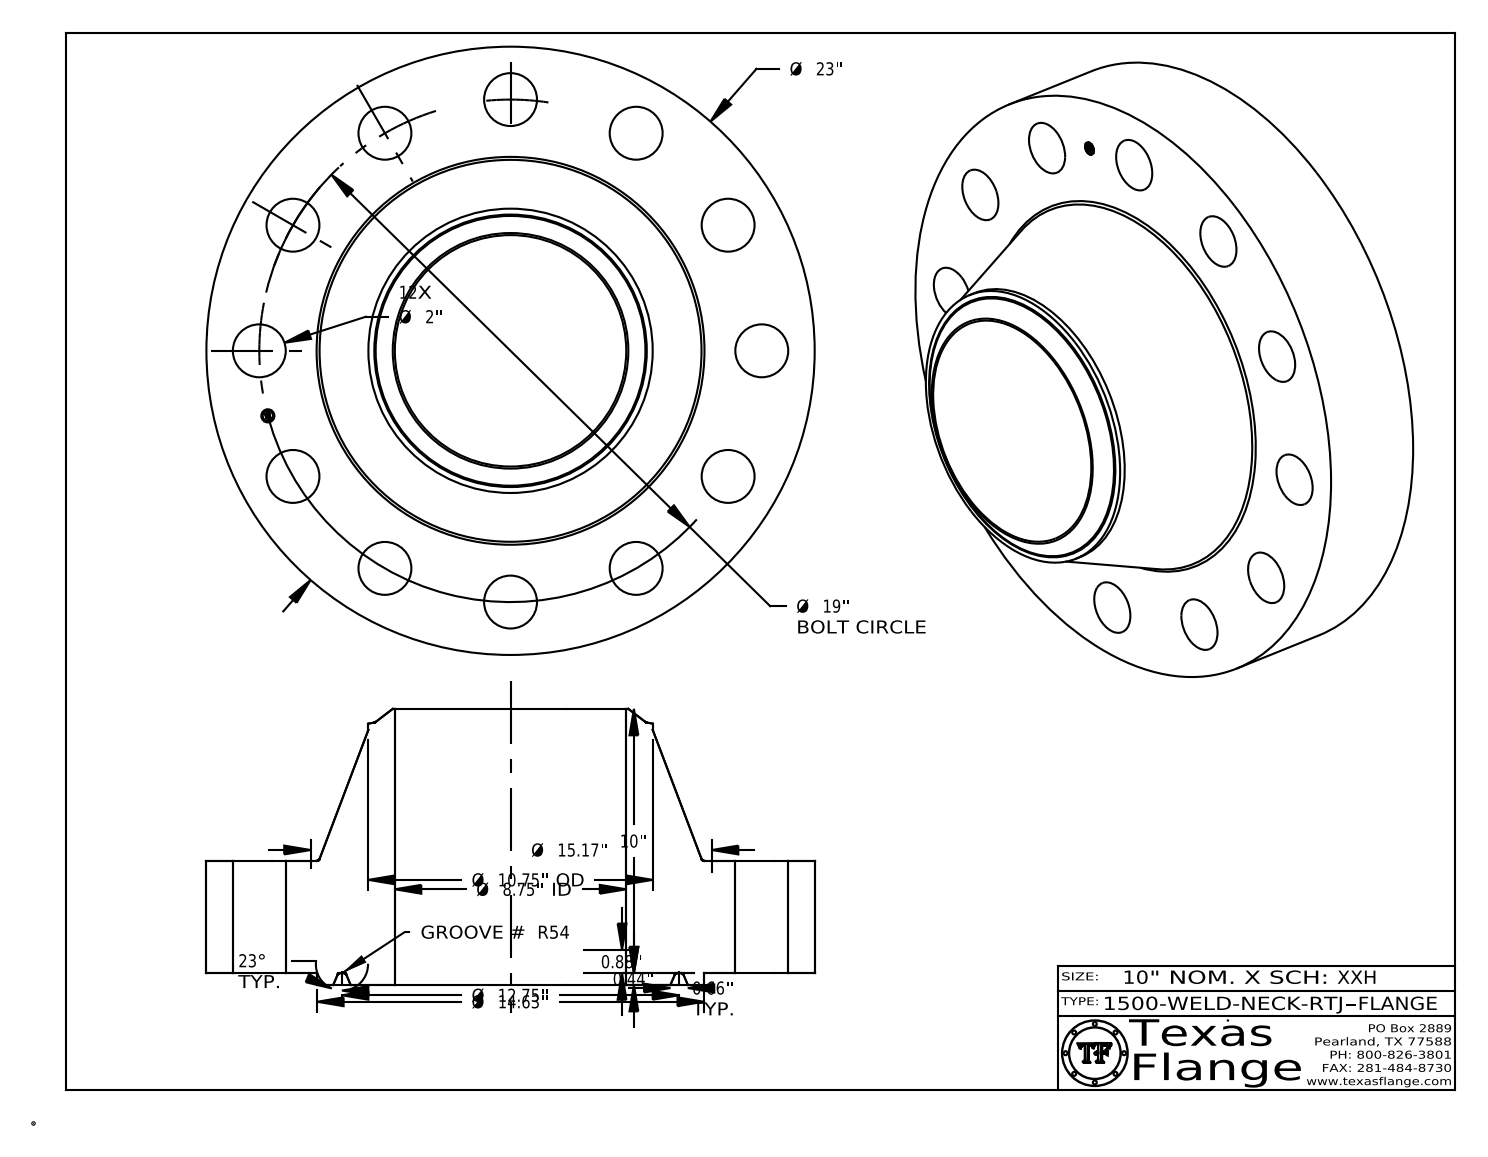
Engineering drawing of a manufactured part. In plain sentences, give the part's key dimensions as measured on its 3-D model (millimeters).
The part is named "1500-WELD-NECK-RTJ". Its 3-D file was written by "CATIA V5 STEP AP214 (AUTOMOTIVE_DESIGN)". It is 1 solid with 441 faces: 371 planar, 52 cylindrical and 18 other. Overall it measures 584.2 by 584.2 by 265.1 millimeters. Its volume is 28 370 000 cubic millimeters and its surface area 1 123 000 square millimeters. Round holes: 12 of diameter 50.8, 1 of diameter 12.6, 1 of diameter 222.3. Round bosses or shafts: 8 of diameter 0.8, 1 of diameter 584.2, 1 of diameter 371.5, 1 of diameter 273.1, 1 of diameter 9.9. The main face-to-face distances are 108, 11.1, 119.1, 265.1, 254, 146.1, 118.7, 107.6, 0.4, 146.4. The hole center spacings are 241.3, 341.2, 417.9, 466.1, 124.9, 482.6, 124.9, 382.9.
